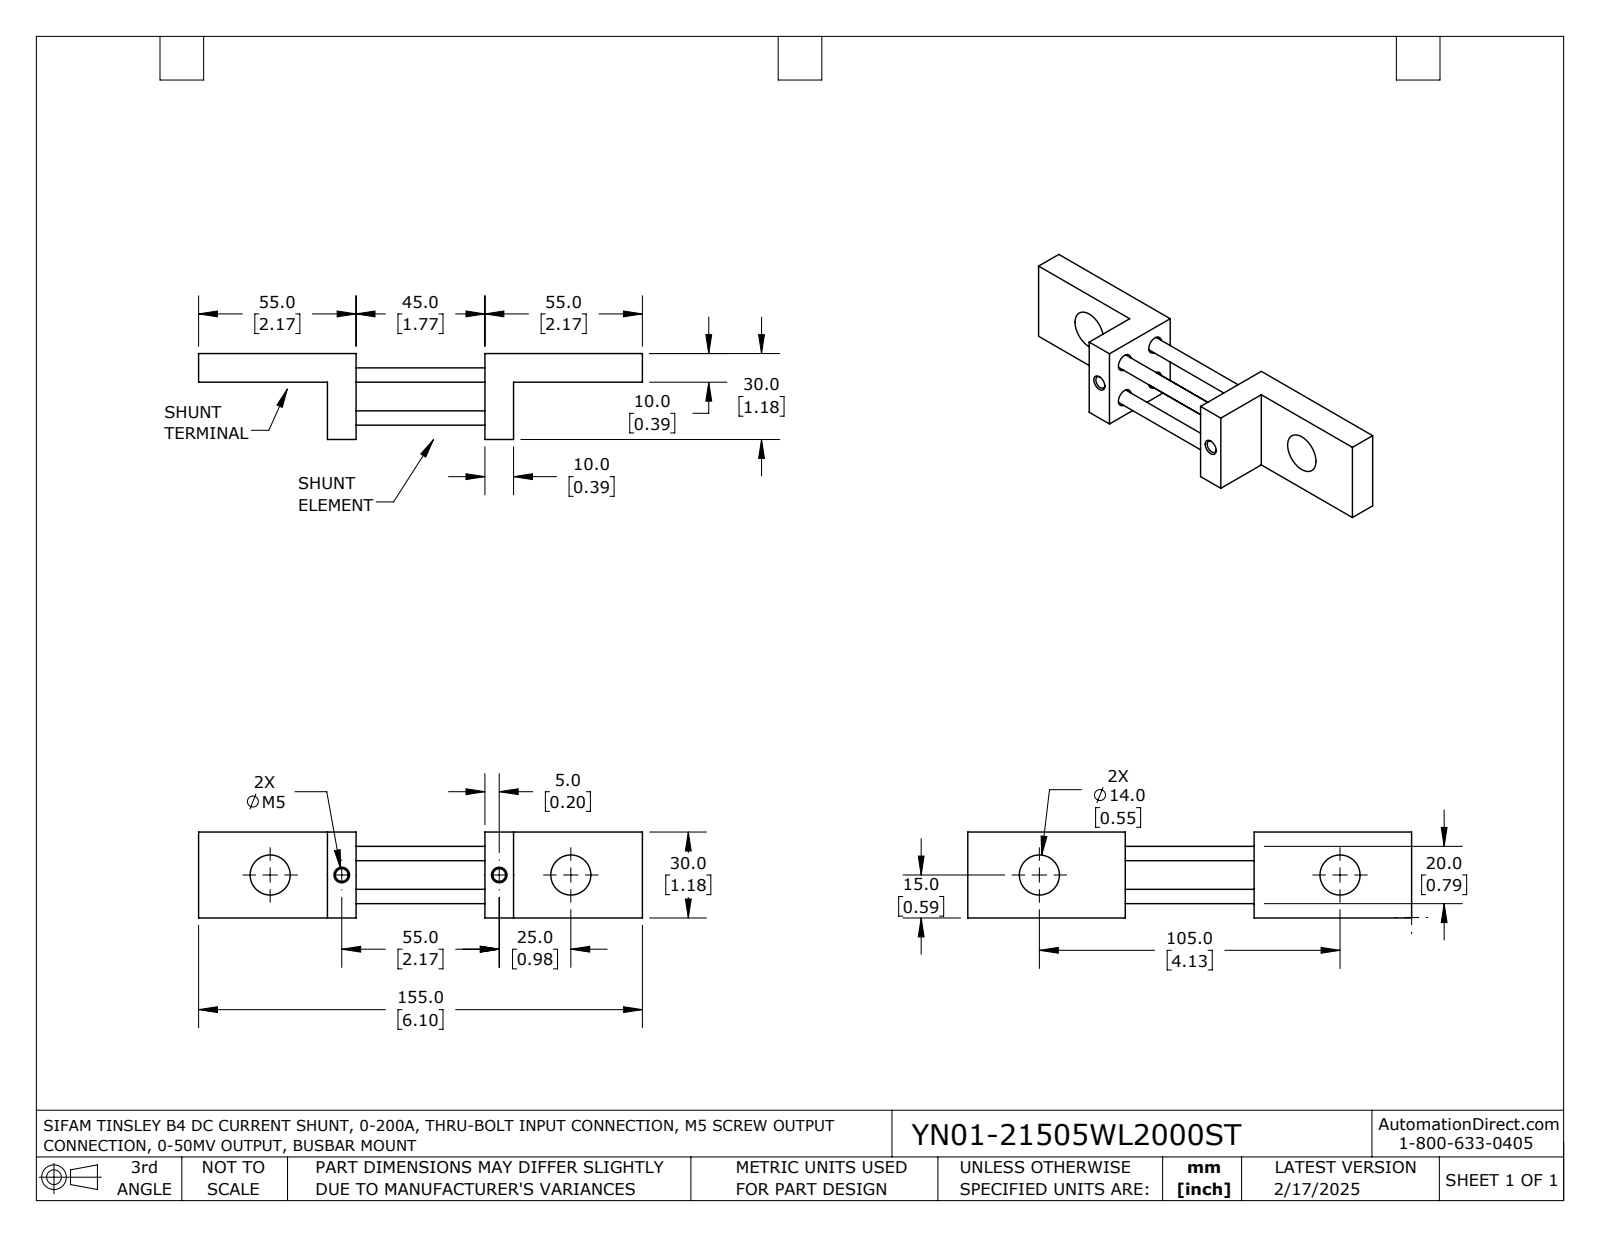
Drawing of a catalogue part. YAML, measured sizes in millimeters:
part_name: "YN01-21505WL2000ST"
step_written_by: "SolidWorks 2021 (AUTOMOTIVE_DESIGN)"
units: millimeters
bodies: {solids: 1, faces: 88, planar: 32, cylindrical: 32, other: 24}
overall_size: [155, 30, 30]
volume: 45060
surface_area: 16950
round_holes:
  - {diameter: 5, count: 4}
  - {diameter: 4.4, count: 2}
  - {diameter: 14, count: 2}
face_to_face_distances: [10, 30, 55, 45, 100, 110, 65, 20, 50, 5]
hole_center_spacings: [15, 21.2, 25, 80, 55, 105]
